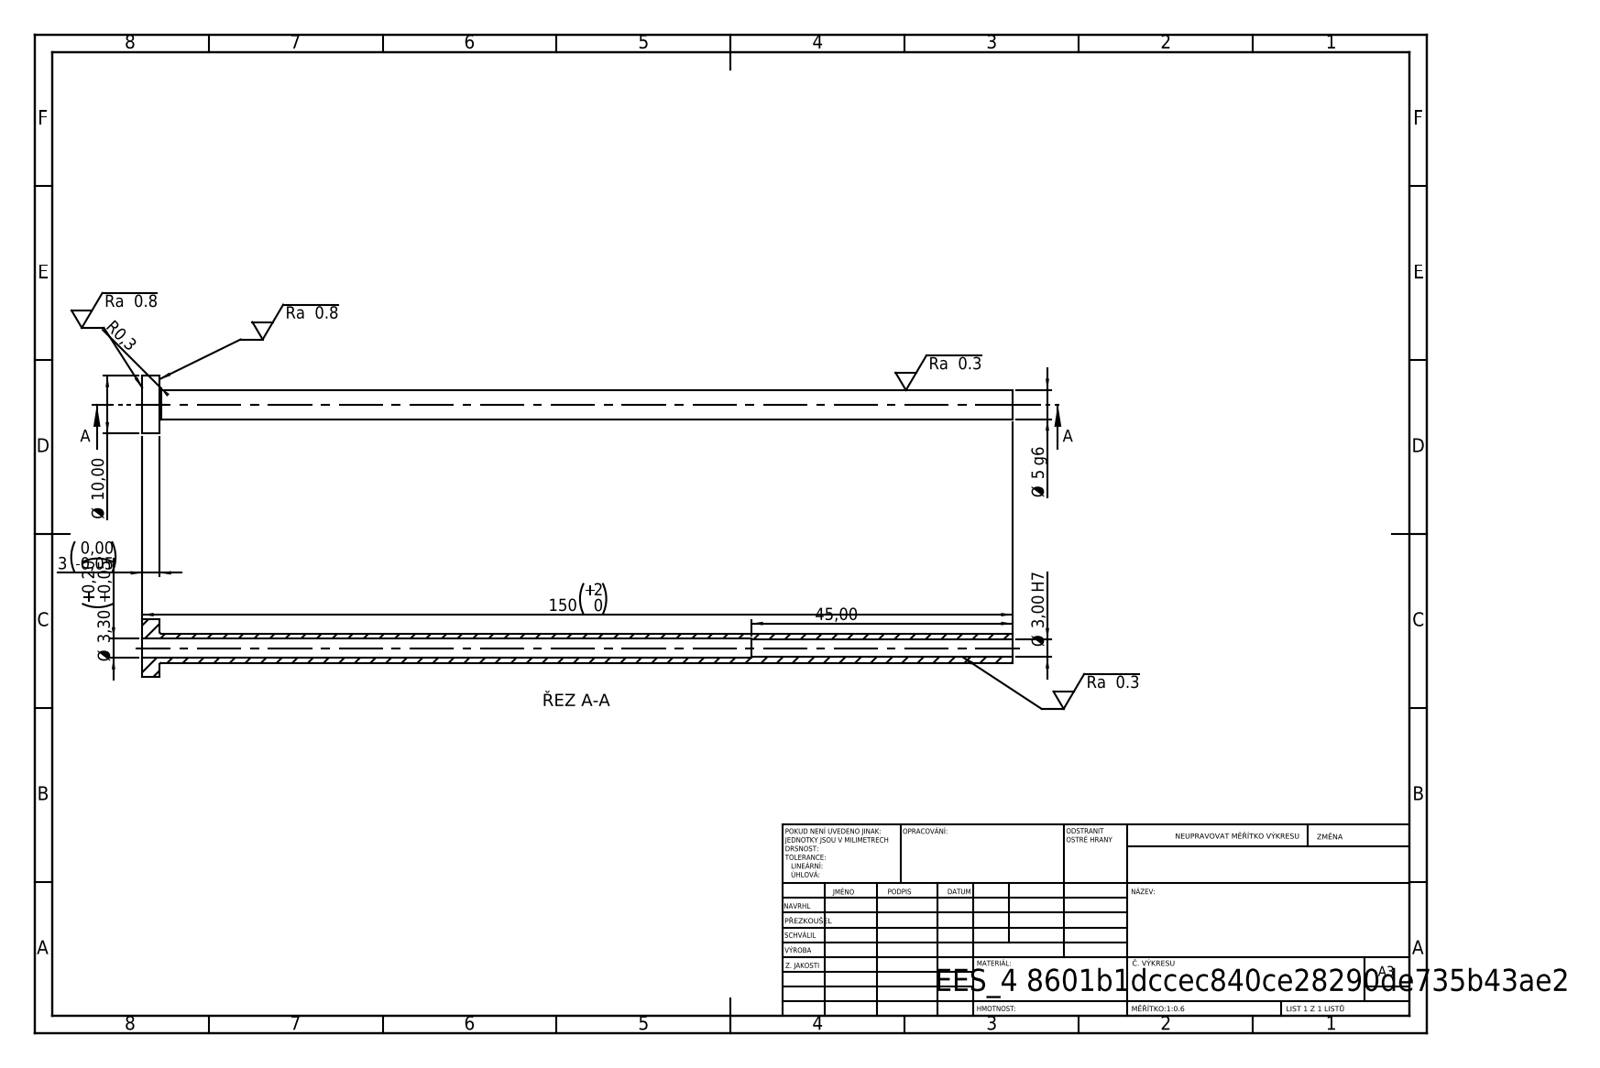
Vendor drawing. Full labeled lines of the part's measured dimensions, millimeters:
STEP written by: SolidWorks 2019 (CONFIG_CONTROL_DESIGN)
Units: millimetres
Bodies: 1 solid, 14 faces (4 planar, 8 cylindrical, 2 other)
Overall size (bounding box): 150 × 10 × 10
Volume: 1 906 mm³ · Surface area: 4 057 mm²
Round holes (diameter × count): ⌀3 ×1, ⌀3.3 ×1
Round bosses / shafts (diameter × count): ⌀10 ×1, ⌀5 ×1
Main face-to-face distances: 3, 150, 147, 105, 102, 45
